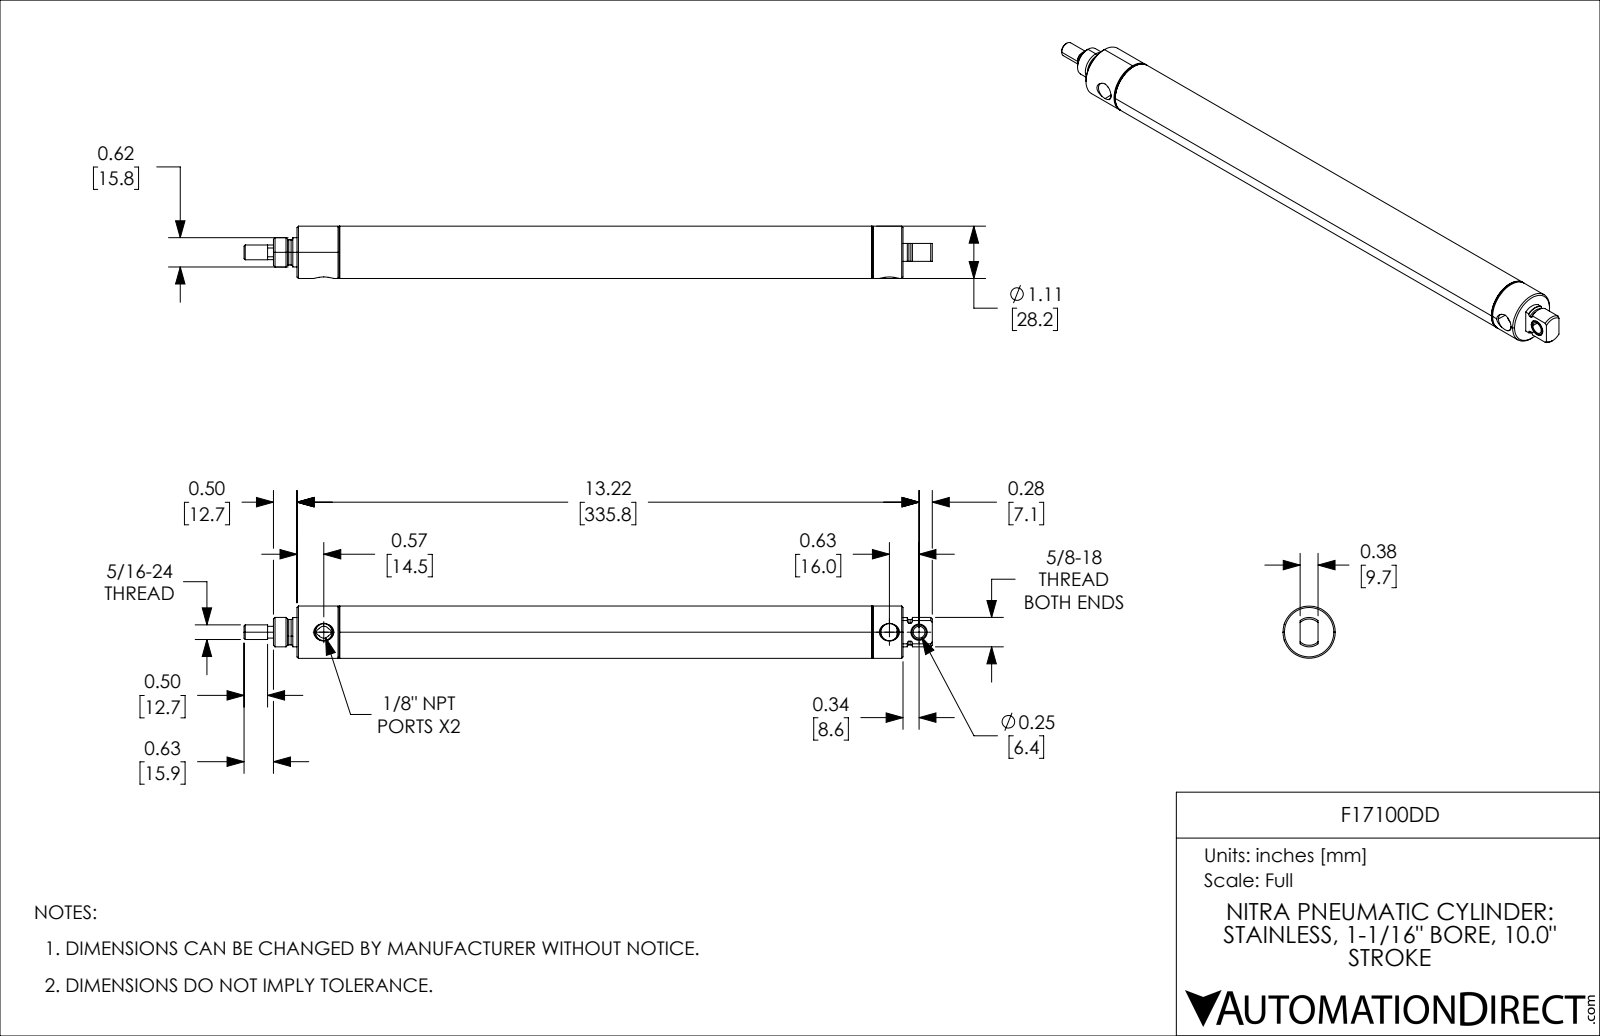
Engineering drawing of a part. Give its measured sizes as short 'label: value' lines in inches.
name: F17100DD_7; F17100DD_11; F17100DD_3; F17100DD_5 (+2 more)
written by: SolidWorks 2021 (CONFIG_CONTROL_DESIGN)
unit: in
bodies: 5 solids, 156 faces (30 planar, 58 cylindrical, 68 other)
size: 14.625 × 1.11 × 1.11
volume: 4.214 in³; area: 112.7 in²
holes: 1× ⌀0.251, 1× ⌀0.336, 1× ⌀0.346, 1× ⌀0.364, 1× ⌀0.375, 1× ⌀0.75, 1× ⌀1.012
bosses: 1× ⌀1.11, 1× ⌀1.072, 1× ⌀0.625, 1× ⌀0.622, 1× ⌀0.539, 1× ⌀0.313, 1× ⌀0.312
rounds: 1× R0.125, 1× R0.269
face distances: 0.875, 10, 10.875, 11.754, 1.754, 0.879, 1.125, 11.125, 12, 12.879
hole spacings: 0.63
